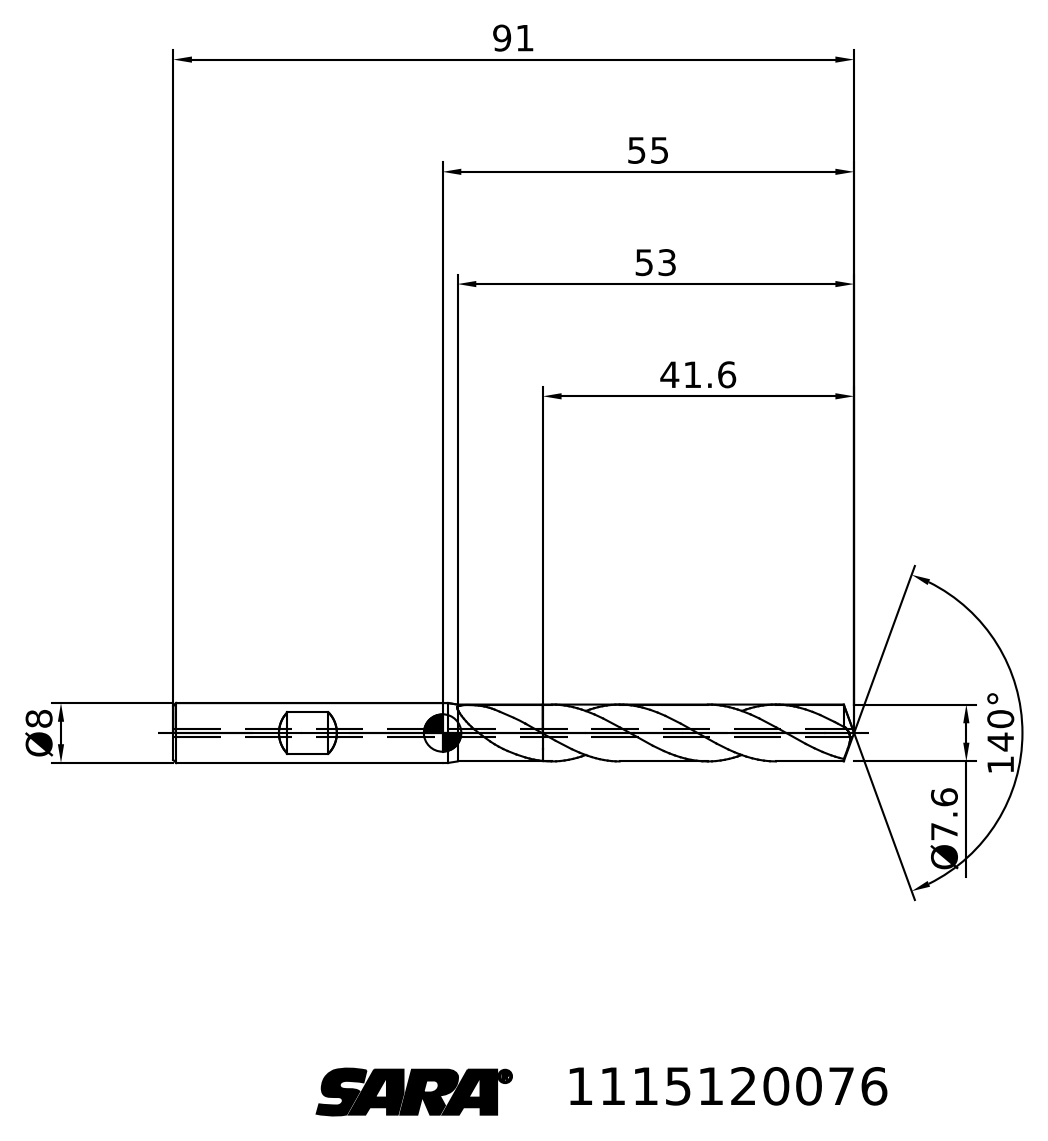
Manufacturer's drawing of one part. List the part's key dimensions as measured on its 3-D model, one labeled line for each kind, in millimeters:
STEP written by: TDM (AUTOMOTIVE_DESIGN)
Units: millimetres
Bodies: 2 solids, 30 faces (6 planar, 0 cylindrical, 24 other)
Overall size (bounding box): 91 × 20 × 10.69
Volume: 3 464 mm³ · Surface area: 2 442 mm²
Main face-to-face distances: 49.4
